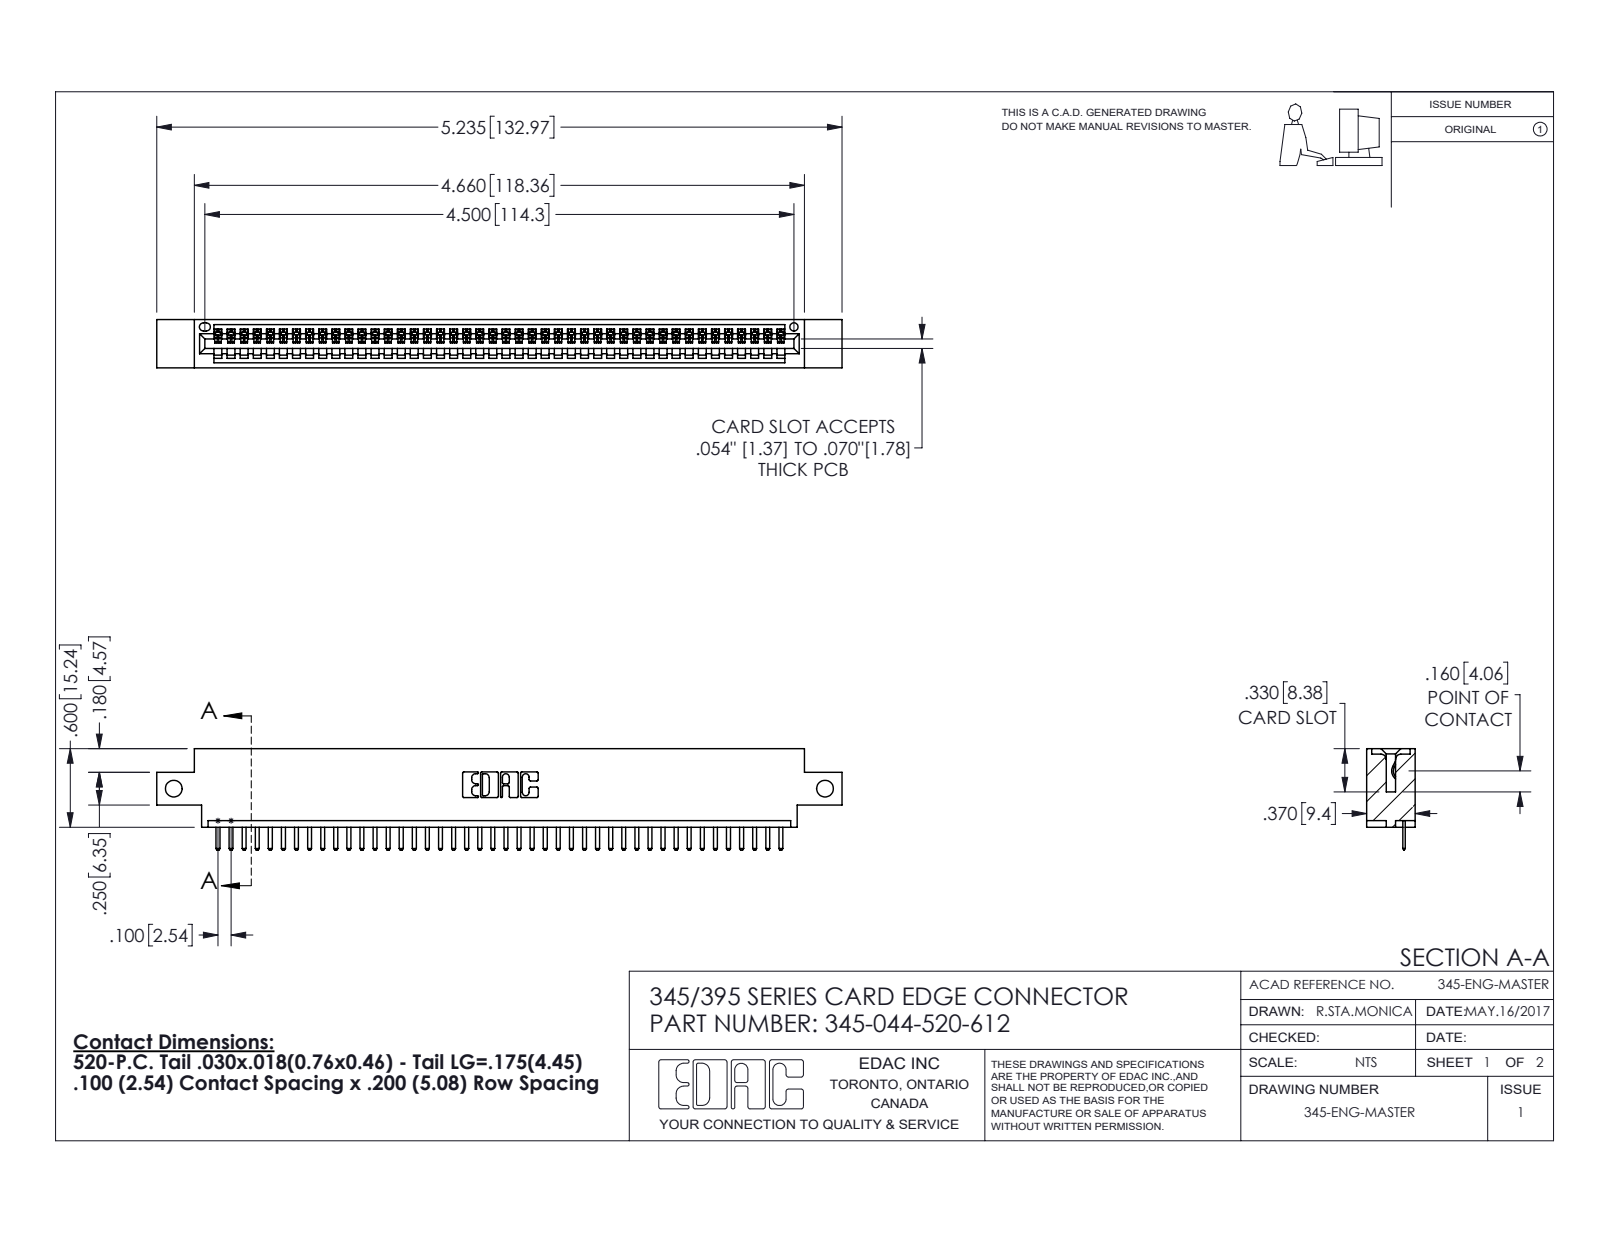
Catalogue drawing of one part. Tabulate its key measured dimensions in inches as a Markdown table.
| quantity | value |
| --- | --- |
| part name | 345-292-001_345-293-120; 345-044-520-612; 345 Part_0.170 Offset - Side Mount |
| STEP written by | SolidWorks 2016 (CONFIG_CONTROL_DESIGN) |
| units | inches |
| bodies | 45 solids, 2858 faces (1932 planar, 926 cylindrical, 0 other) |
| overall size | 5.235 × 0.775 × 0.37 |
| volume | 0.752 in³ |
| surface area | 24.75 in² |
| round holes (diameter × count) | 0.128 × 2, 0.064 × 1 |
| partial cylindrical surfaces (radius × count) | 0.01 × 90, 0.006 × 88, 0.01 × 22, 0.007 × 6, 0.031 × 6, 0.026 × 3, 0.031 × 2, 0.04 × 2 |
| main face-to-face distances | 0.072, 0.298, 0.37, 0.2, 0.098, 0.272, 0.025, 0.225, 0.072, 0.175 |
| hole center spacings | 4.975 |
